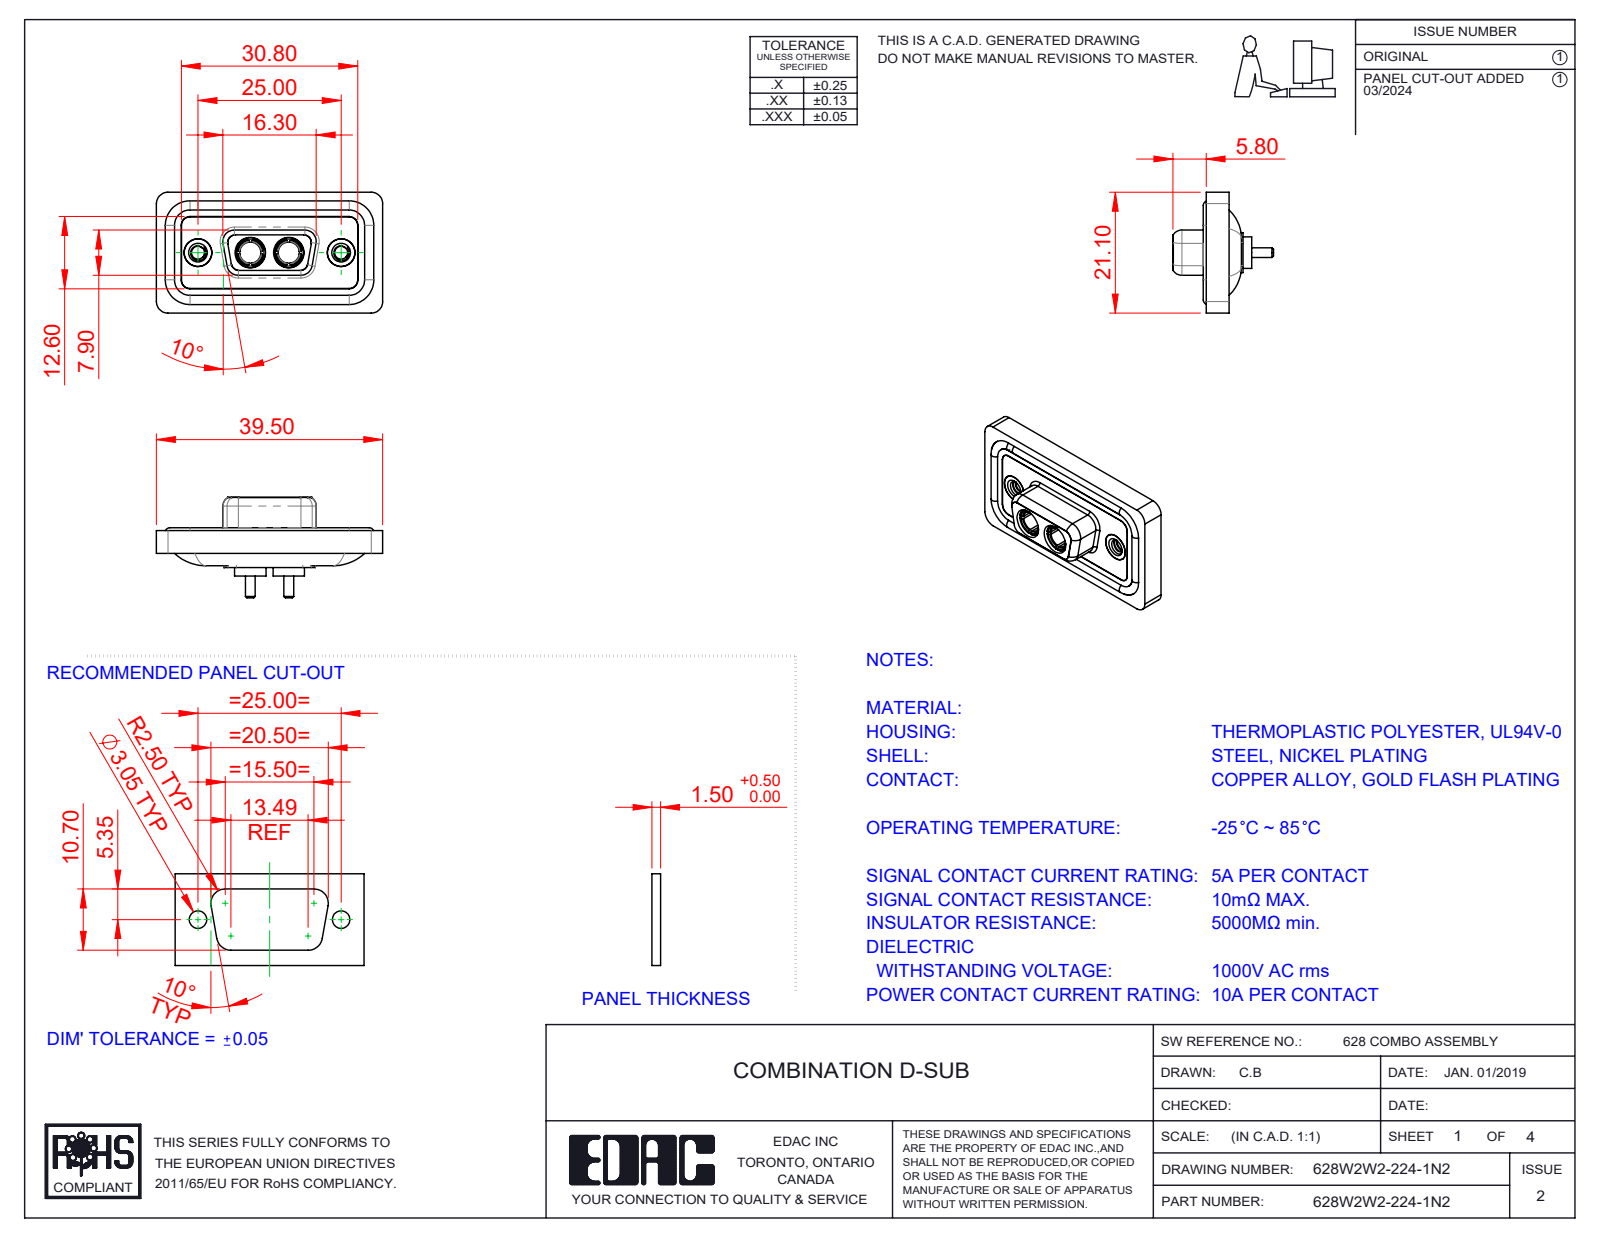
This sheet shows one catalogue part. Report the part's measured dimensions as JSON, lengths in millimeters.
{"part_name": "628Combo Shell Rear_09 Contacts; 628Combo Waterproof Housing_09 Contacts; 628Combo Threaded Rivet_2; Power Socket_10A S (+3 more)", "step_written_by": "SolidWorks 2023 (CONFIG_CONTROL_DESIGN)", "units": "millimeters", "bodies": {"solids": 11, "faces": 534, "planar": 163, "cylindrical": 234, "other": 137}, "overall_size": [39.5, 21.1, 17.55], "volume_mm3": 4683, "surface_area_mm2": 7611, "round_holes": [[4.85, 4], [2.26, 2], [3.7, 2], [4, 2], [4.05, 2], [5, 2], [5.3, 2]], "round_bosses_or_shafts": [[1.6, 4], [5.5, 2], [5.2, 2], [4.96, 2], [4.95, 2], [4.8, 2], [4.75, 2], [3.75, 2]], "partial_cylinders_radius": [[1.5, 22], [2, 18], [1.35, 8], [1.6, 8], [0.25, 4], [0.5, 4], [0.6, 4], [0.65, 4]], "face_to_face_distances": [0.4, 1.8, 1.1, 2.9, 0.5, 1.6, 5.65, 1.5, 7.45, 5.35], "hole_center_spacings": [9.14, 15.86, 6.72, 25]}
